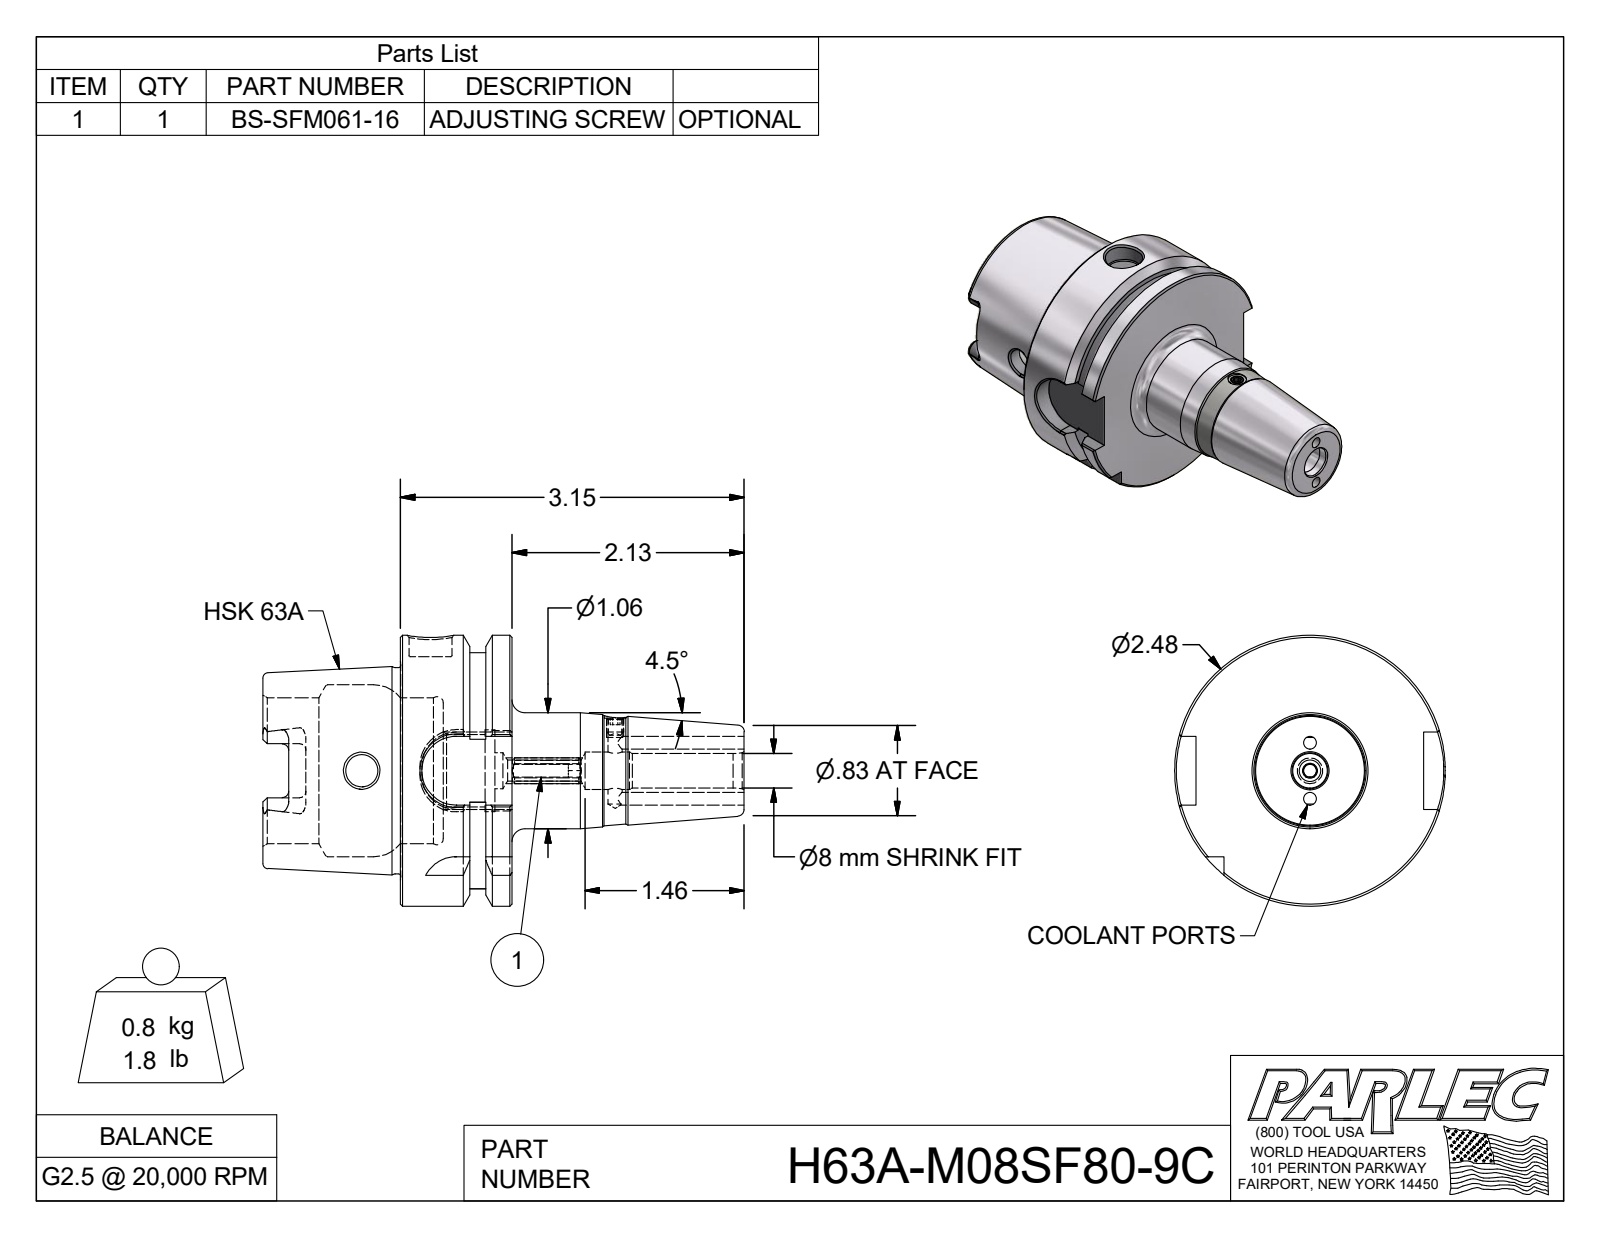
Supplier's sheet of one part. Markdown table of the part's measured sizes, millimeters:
| quantity | value |
| --- | --- |
| part name | H63A-M08SF80-9C; BS-SFM061-16; 029-060 |
| STEP written by | Autodesk Inventor 2018 (AUTOMOTIVE_DESIGN) |
| units | millimeters |
| bodies | 3 solids, 189 faces (77 planar, 46 cylindrical, 66 other) |
| overall size | 112 × 63 × 63 |
| volume | 105 200 mm³ |
| surface area | 28 760 mm² |
| round holes (diameter × count) | 3 × 3, 3.3 × 1, 4.9 × 1, 5 × 1, 7.5 × 1, 8 × 1, 8.4 × 1, 8.7 × 1, 10 × 1, 16.9 × 1, 19 × 1, 34 × 1 |
| round bosses / shafts (diameter × count) | 63 × 1, 48 × 1, 27 × 1, 4 × 1 |
| partial cylindrical surfaces (radius × count) | 1.5 × 6, 2.9 × 4, 8 × 4, 3 × 1, 27.5 × 1 |
| main face-to-face distances | 26, 6.1, 9.9, 10, 58, 16, 32, 54, 42, 51.9 |
| hole center spacings | 6.5, 13, 43 |
